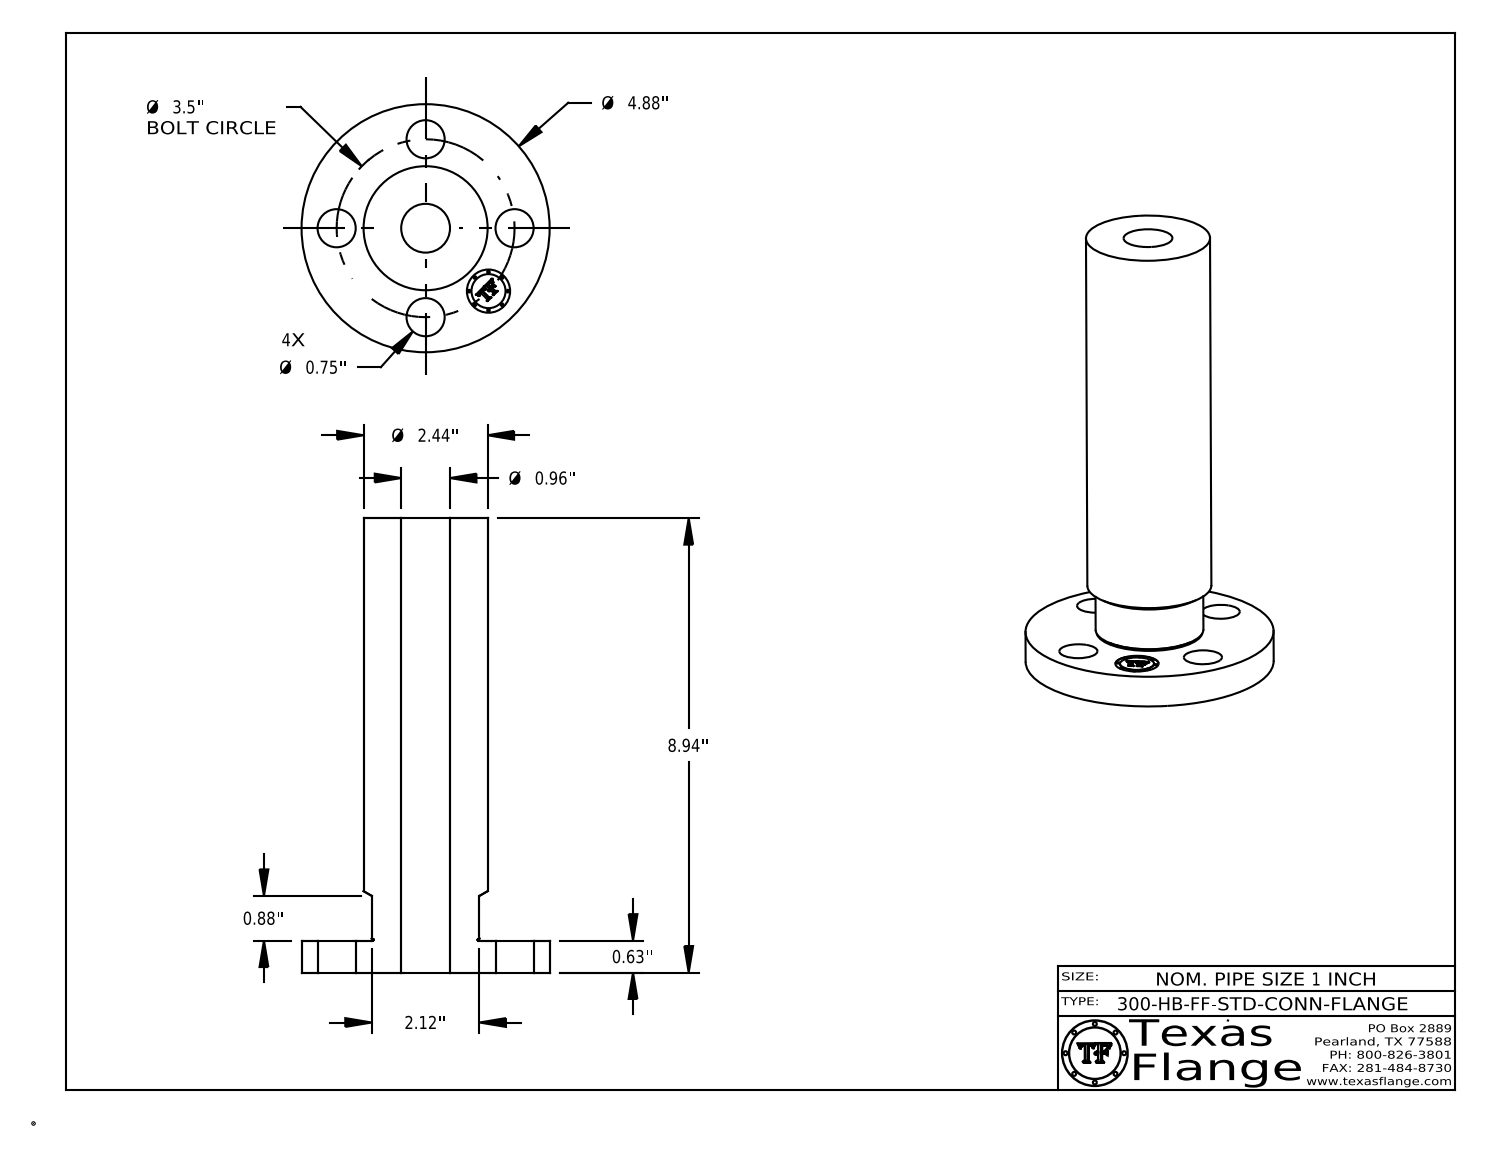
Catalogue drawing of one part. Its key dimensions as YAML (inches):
part_name: "1-300-HB-FF-STD-CONN-FLANGE"
step_written_by: "CATIA V5 STEP AP214 (AUTOMOTIVE_DESIGN)"
units: inches
bodies: {solids: 1, faces: 410, planar: 368, cylindrical: 36, other: 6}
overall_size: [8.938, 4.88, 4.88]
volume: 41.95
surface_area: 139.8
round_holes:
  - {diameter: 0.75, count: 4}
  - {diameter: 0.85, count: 1}
  - {diameter: 0.96, count: 1}
round_bosses_or_shafts:
  - {diameter: 0.051, count: 8}
  - {diameter: 4.88, count: 1}
  - {diameter: 2.44, count: 1}
  - {diameter: 2.12, count: 1}
  - {diameter: 0.67, count: 1}
face_to_face_distances: [0.628, 8.937, 8.31, 0.622, 8.315, 0.016, 0.254, 0.249, 0.046, 0.165]
hole_center_spacings: [1.75, 2.475, 1.339, 3.233, 3.5]
